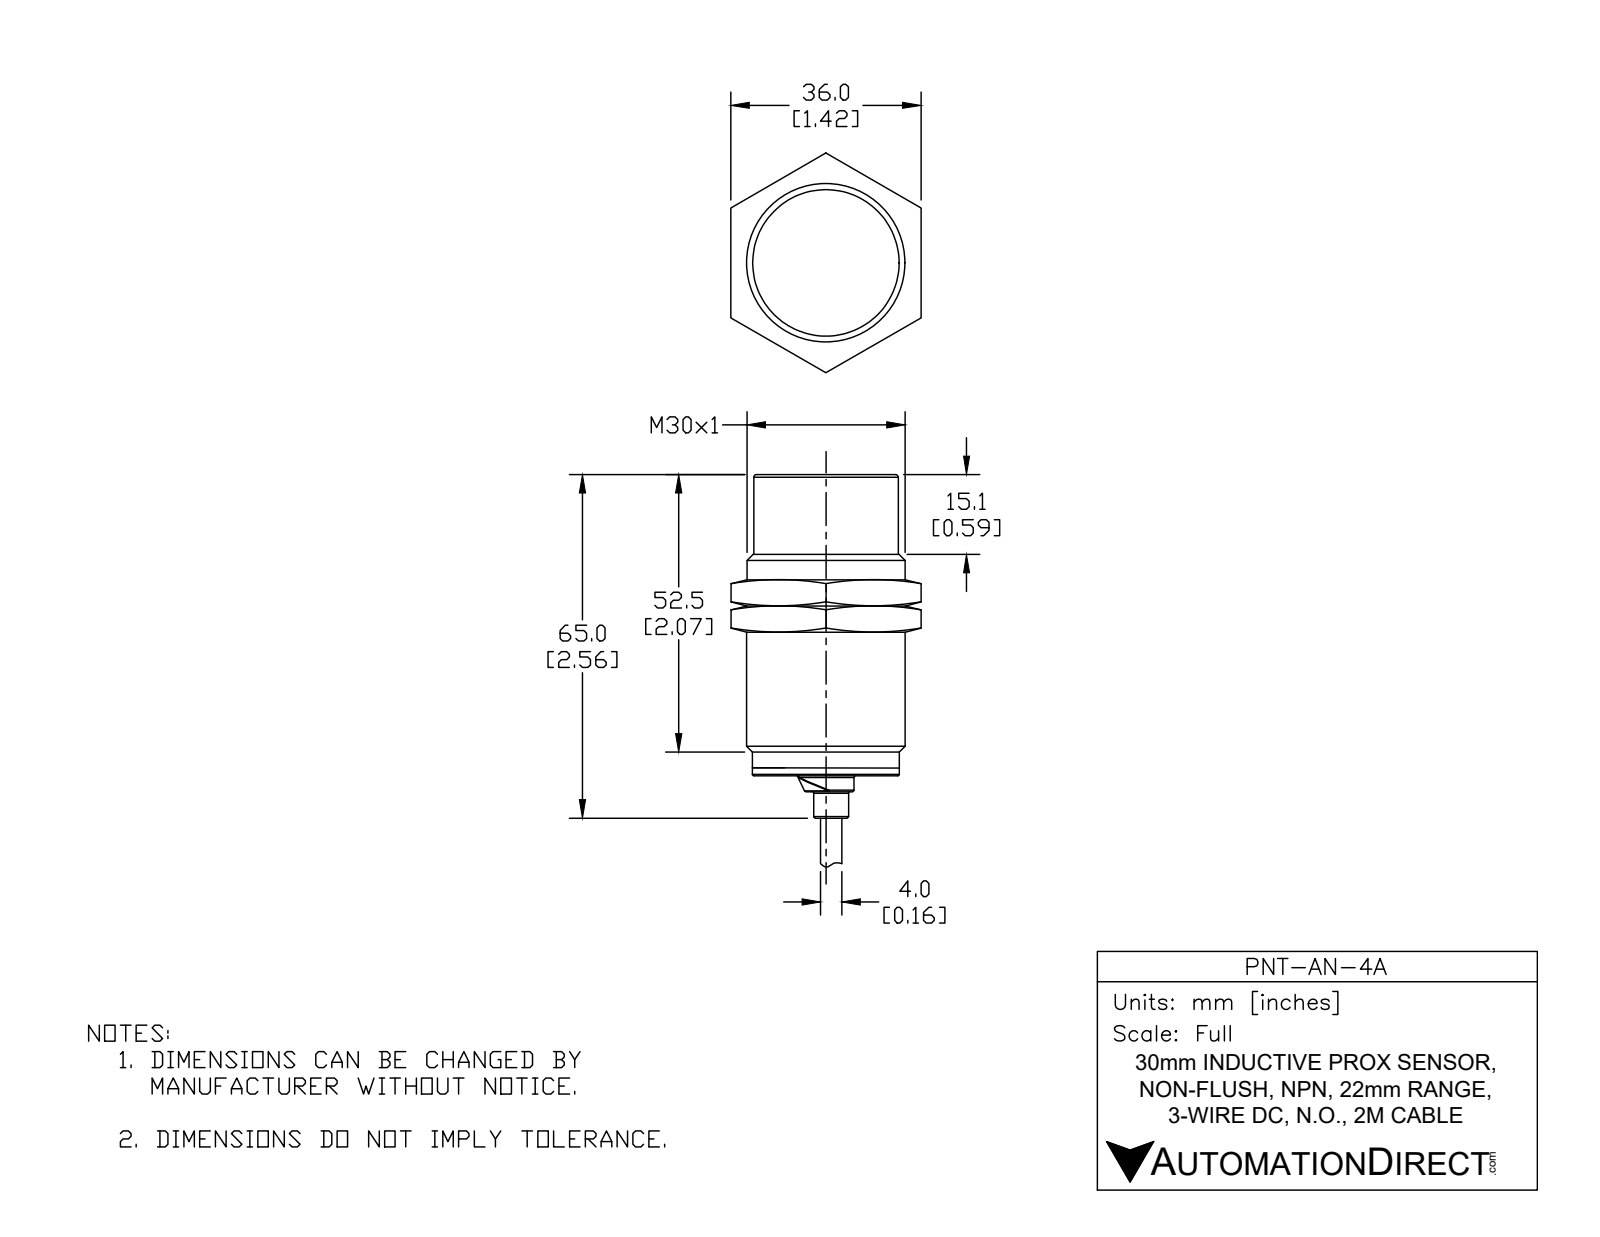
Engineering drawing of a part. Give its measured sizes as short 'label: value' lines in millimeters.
name: PNT-AN-4A
written by: SolidWorks 2017 (AUTOMOTIVE_DESIGN)
unit: mm
bodies: 1 solid, 74 faces (14 planar, 30 cylindrical, 30 other)
size: 115.8 × 30 × 30
volume: 40 750 mm³; area: 7 677 mm²
holes: 1× ⌀4.1
bosses: 6× ⌀1.2, 1× ⌀30, 1× ⌀27.8, 1× ⌀27.8, 1× ⌀10.6, 1× ⌀6.6, 1× ⌀4
rounds: 1× R2
face distances: 57, 60, 3, 57.9, 65, 8, 5, 115.8, 58.8, 55.8
